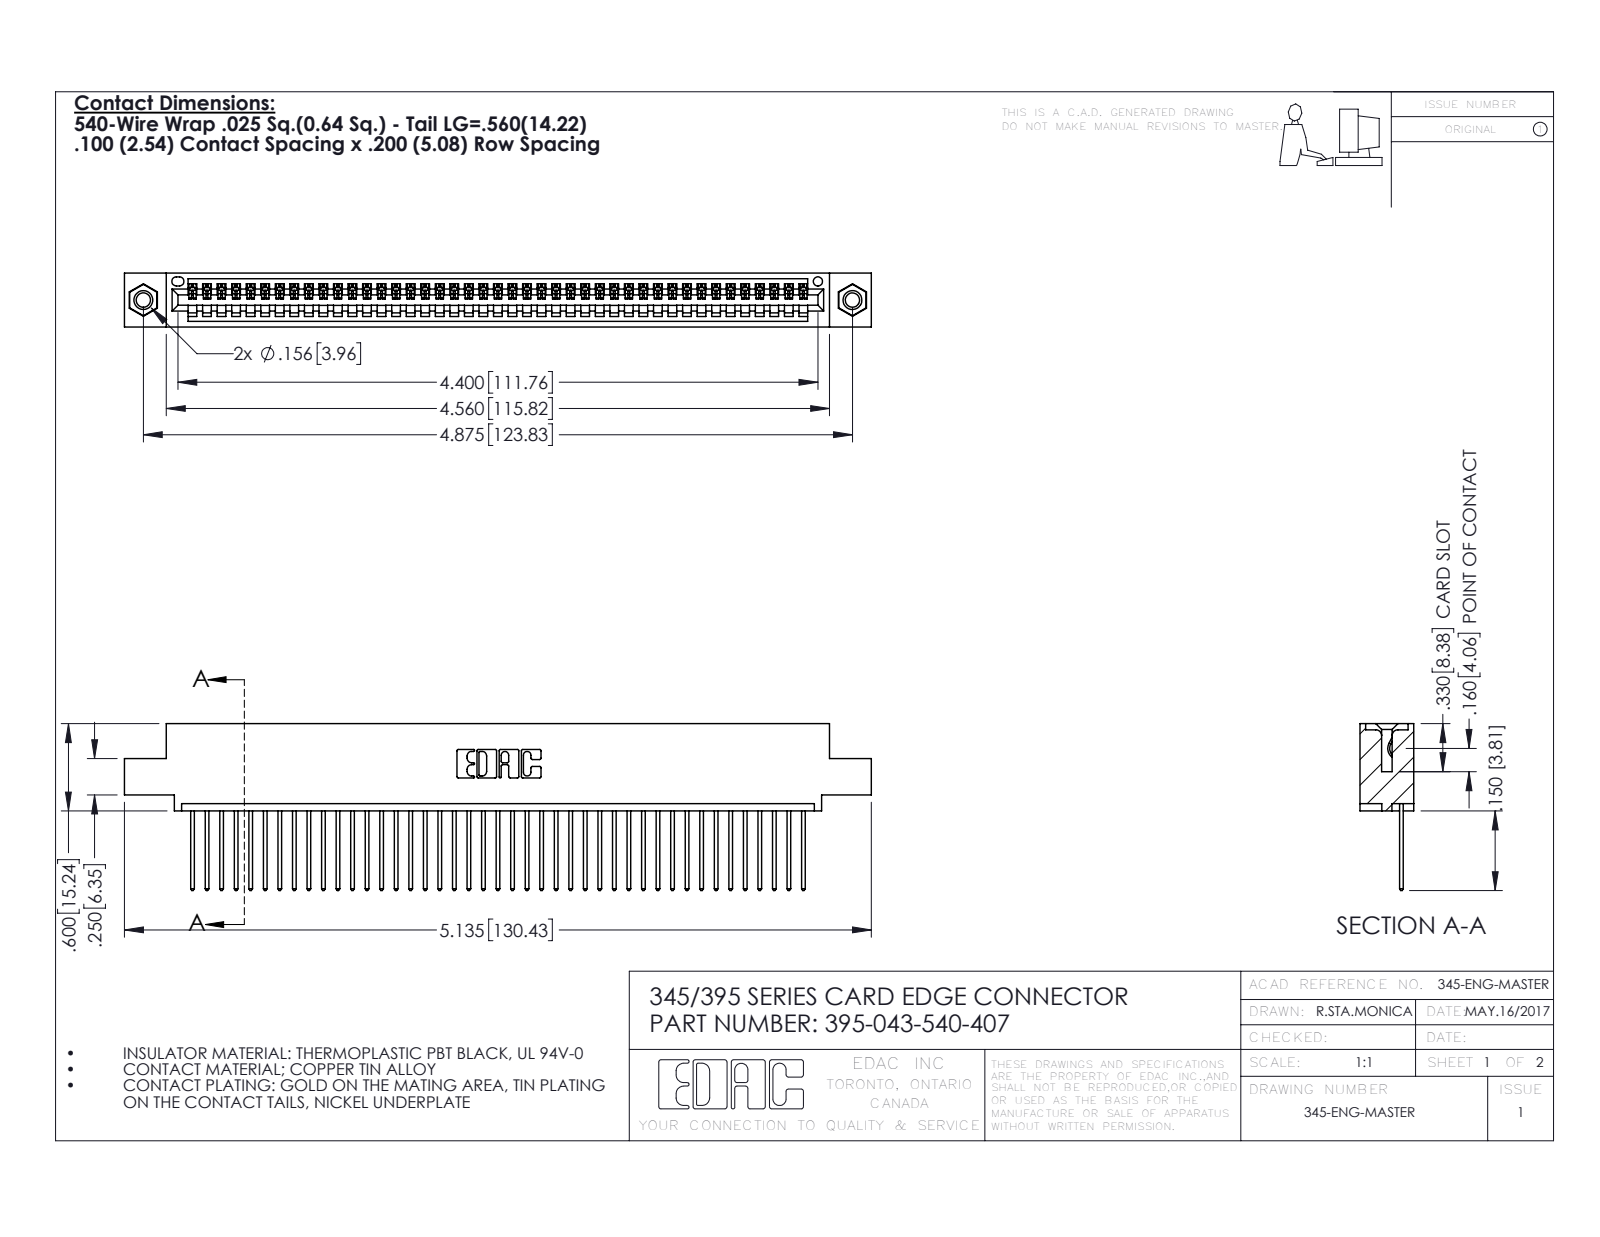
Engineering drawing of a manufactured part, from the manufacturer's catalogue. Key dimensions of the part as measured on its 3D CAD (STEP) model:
Part name (STEP PRODUCT): 345-292-001_345-293-140; 345 Part_0.110 Offset - 0.156 Dia-TI; 345-250-001_345-250-005-103; 395-043-540-407
STEP written by: SolidWorks 2016 (CONFIG_CONTROL_DESIGN)
Units: inches
Bodies: 46 solids, 2684 faces (1836 planar, 832 cylindrical, 16 other)
Overall size (bounding box): 5.135 × 1.147 × 0.37
Volume: 0.755 in³ · Surface area: 26.32 in²
Round holes (diameter × count): ⌀0.098 ×2, ⌀0.125 ×2, ⌀0.156 ×2, ⌀0.064 ×1
Round bosses / shafts (diameter × count): ⌀0.155 ×2
Partial cylindrical surfaces — rounded edges, fillets, slot ends (radius × count): R0.006 ×86, R0.01 ×86, R0.01 ×22, R0.007 ×6, R0.031 ×6, R0.026 ×3, R0.031 ×2, R0.04 ×2
Main face-to-face distances: 0.072, 0.298, 0.37, 0.098, 0.272, 0.025, 0.2, 0.225, 0.149, 0.072
Hole centre spacings: 0.27, 4.639, 4.875
